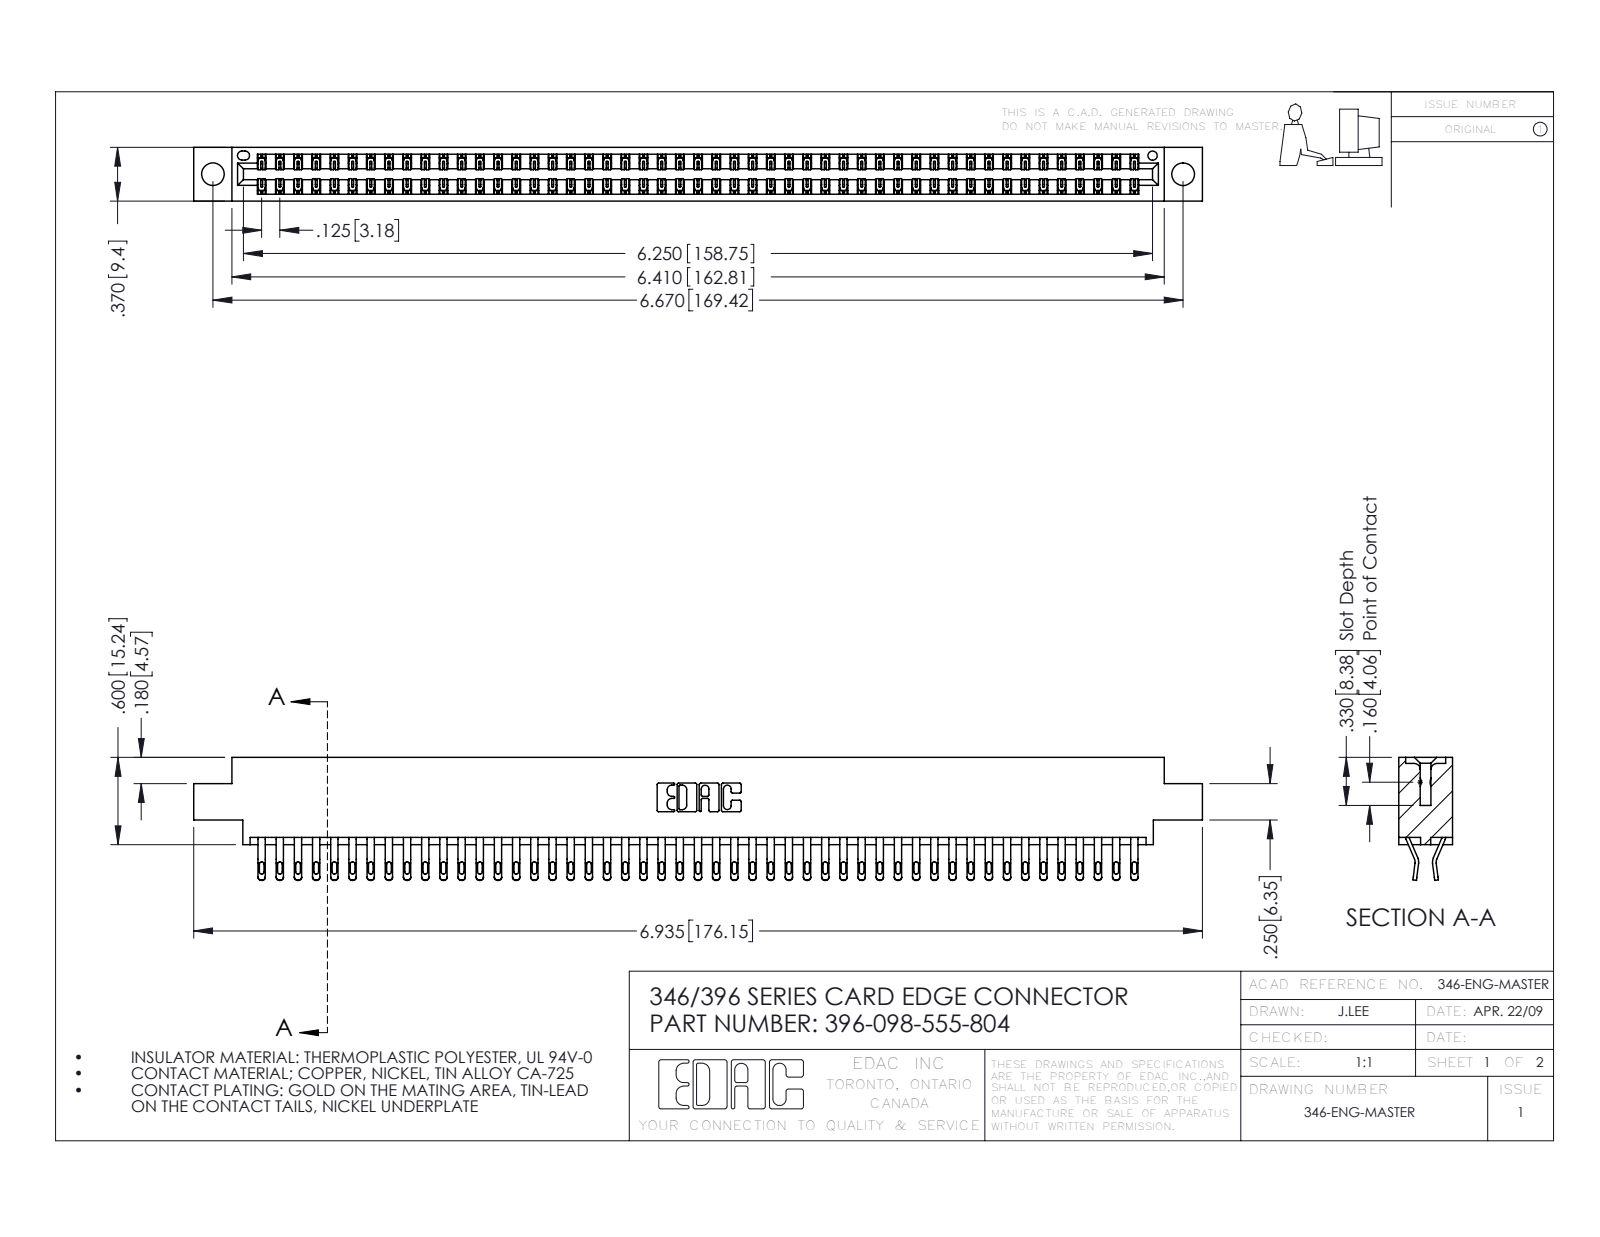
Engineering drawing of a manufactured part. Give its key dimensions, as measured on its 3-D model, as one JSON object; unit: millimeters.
{"part_name": "396-098-555-804; 346 Part_0.170 Offset - 0.156 Dia-TH; 345-292-001_555 Tail", "step_written_by": "SolidWorks 2016 (CONFIG_CONTROL_DESIGN)", "units": "millimeters", "bodies": {"solids": 99, "faces": 5810, "planar": 3314, "cylindrical": 2496, "other": 0}, "overall_size": [176.1, 21.5, 9.4], "volume_mm3": 17270, "surface_area_mm2": 24860, "round_holes": [[4, 2], [1.6, 1]], "partial_cylinders_radius": [[0.4, 196], [0.5, 196], [0.2, 147], [0.3, 22], [0.2, 6], [0.8, 6], [0.7, 3], [0.3, 2]], "face_to_face_distances": [1.2, 8.2, 9.4, 6.4, 0.6, 1.8, 7.6, 7, 3.8, 5.6], "hole_center_spacings": [6.2, 164.1, 169.4]}
